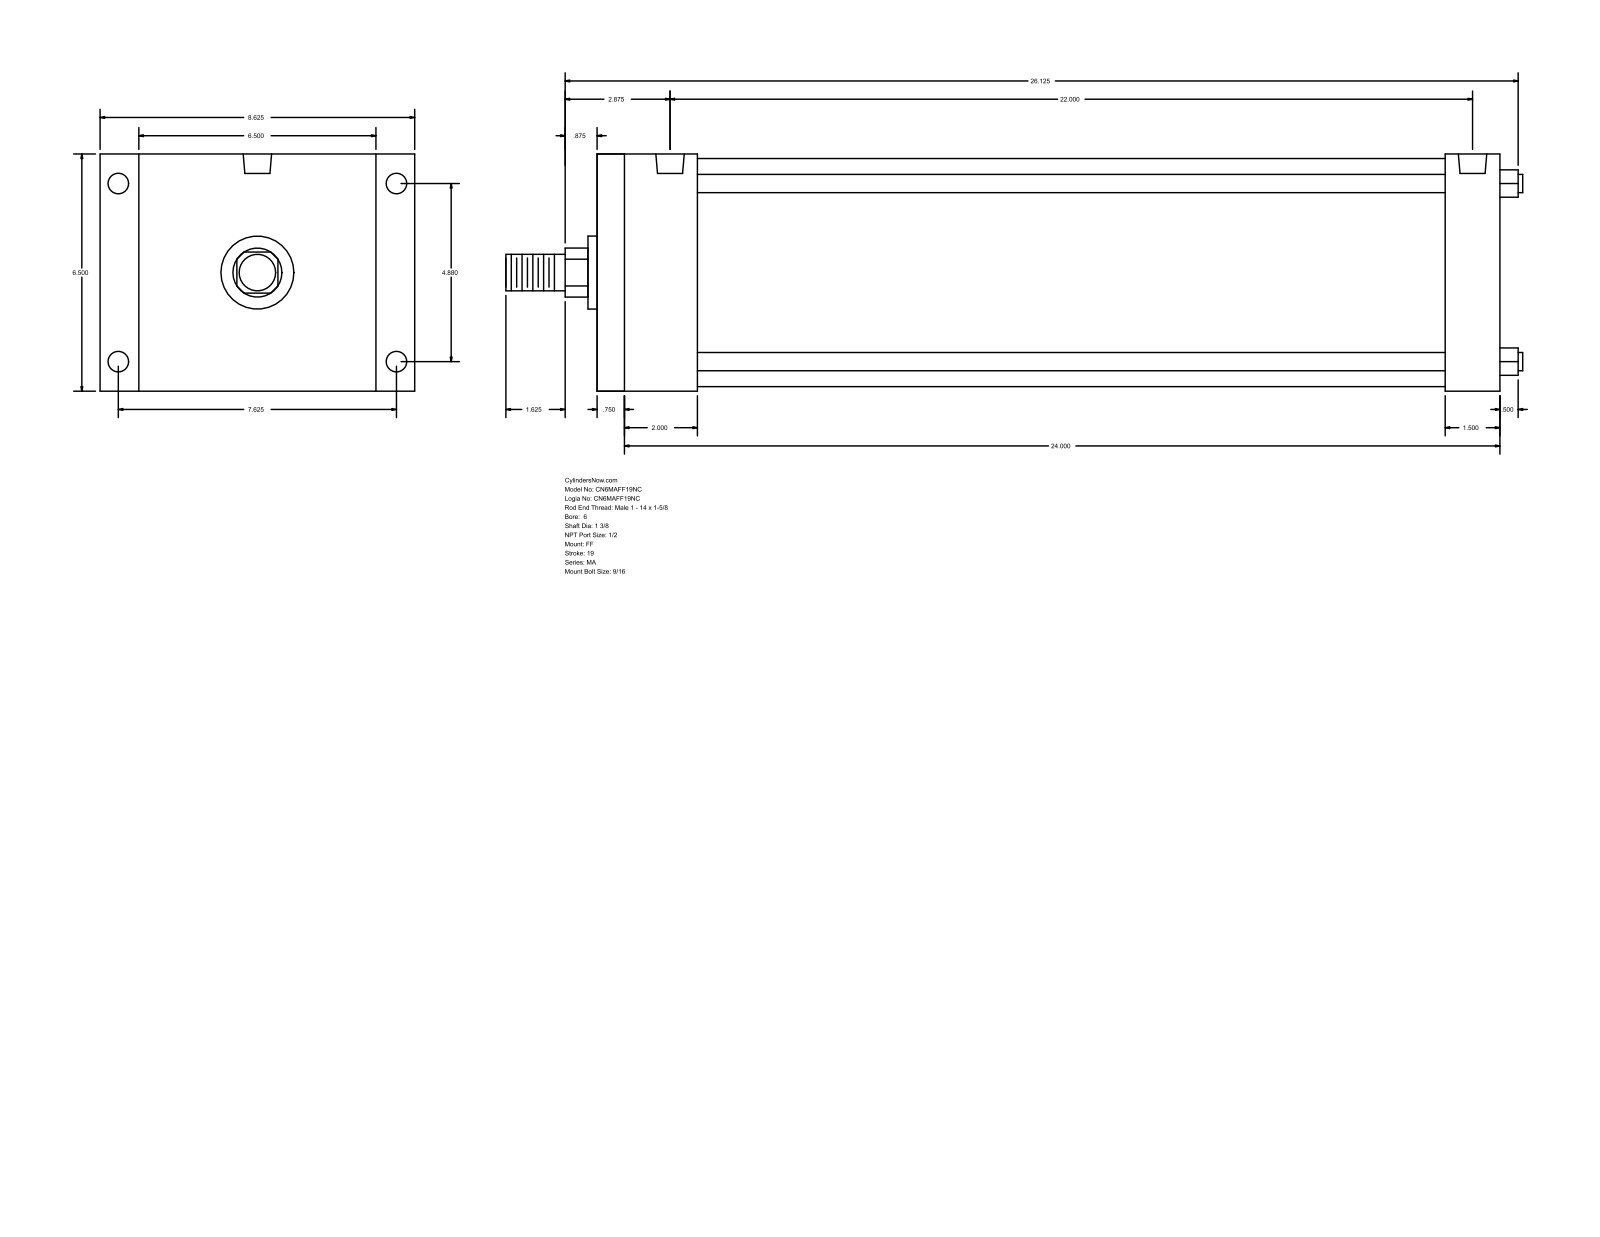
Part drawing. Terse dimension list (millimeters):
name: MA_FF__0600_1.375
written by: GSSL Pune (CONFIG_CONTROL_DESIGN)
unit: mm
bodies: 0 solids, 92 faces (64 planar, 28 cylindrical, 0 other)
size: 708.02 × 219.07 × 165.1
holes: 4× ⌀14.29, 4× ⌀17.46, 2× ⌀19.77
bosses: 4× ⌀12.7, 1× ⌀158.75, 1× ⌀50.8, 1× ⌀34.92, 1× ⌀25.4
rounds: 1× R17.06
face distances: 165.1, 628.65, 15.87, 612.78, 66.67, 50.8, 561.98, 590.54, 574.67, 523.87
hole spacings: 123.96, 193.68, 229.95, 561.98, 3.18, 558.8
